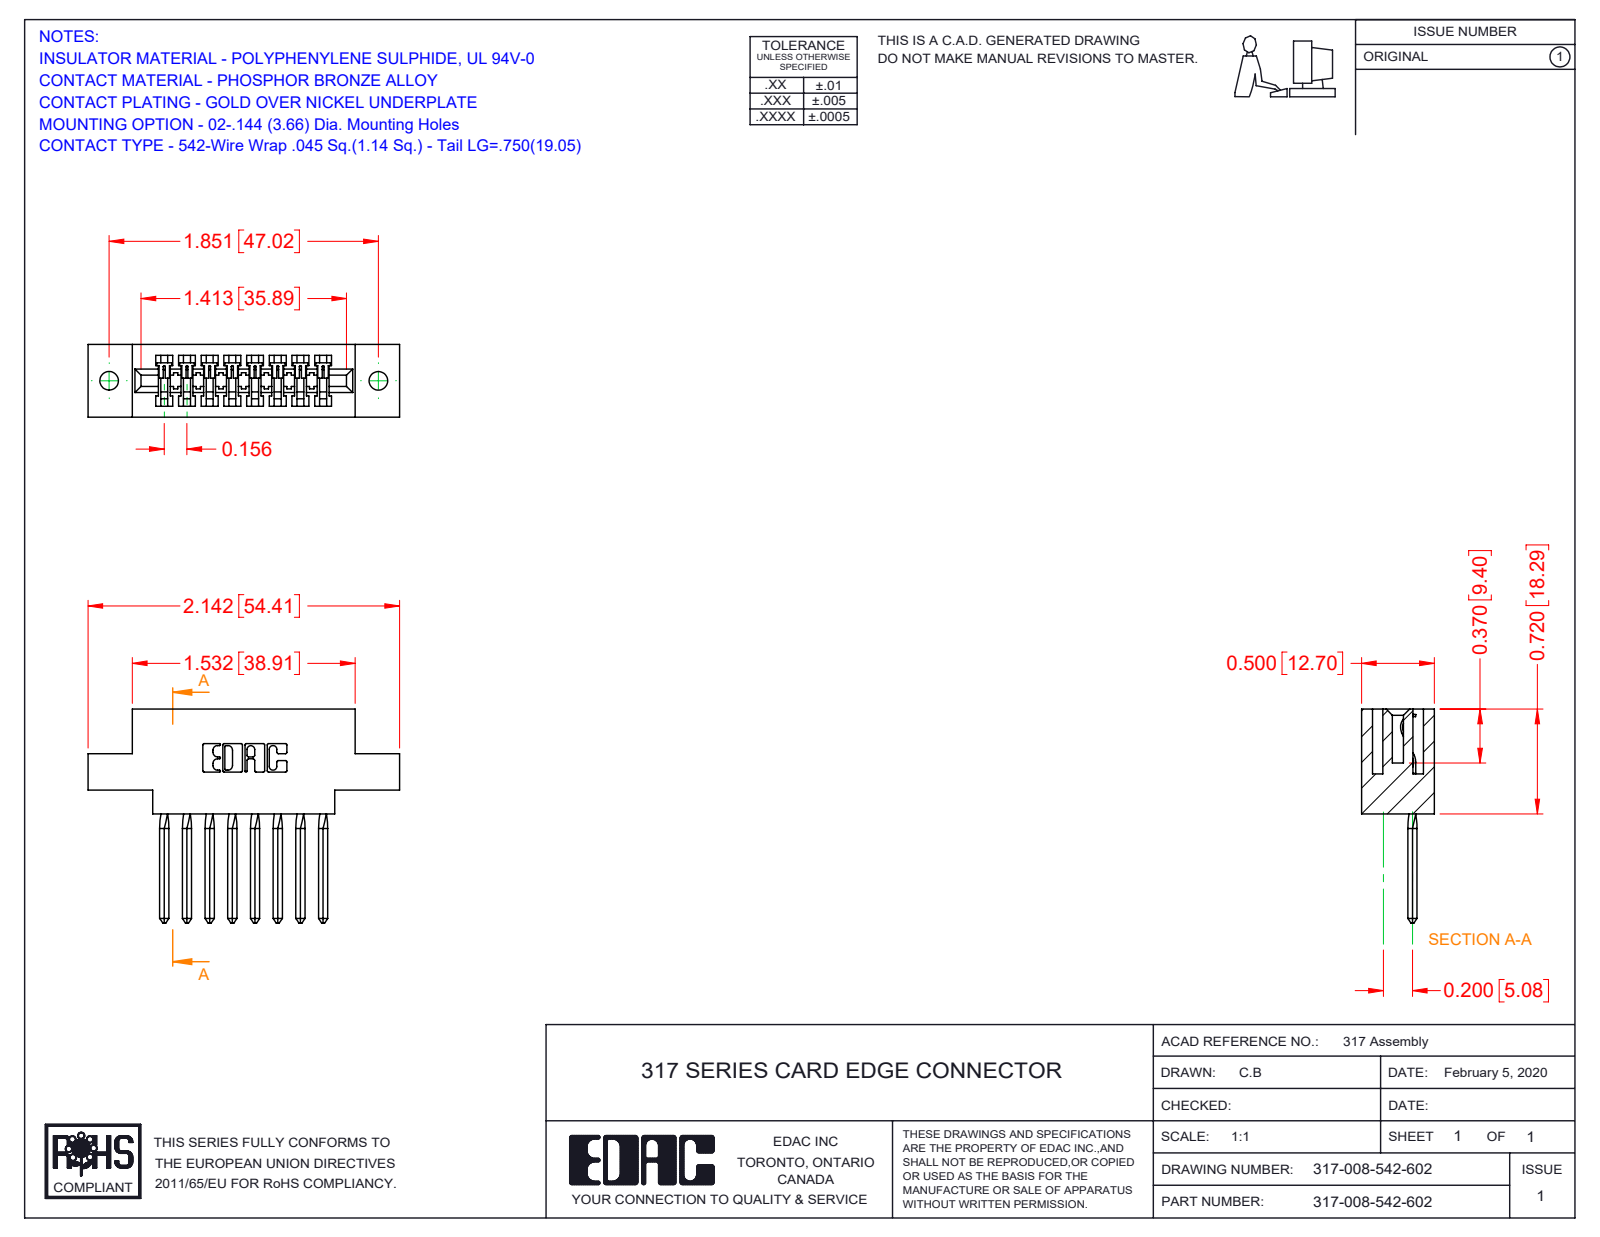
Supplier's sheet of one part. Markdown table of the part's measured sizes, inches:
| quantity | value |
| --- | --- |
| part name | 317-290-003_542; 317-008-542-602; 317 Part_.144 Dia |
| STEP written by | SolidWorks 2016 (CONFIG_CONTROL_DESIGN) |
| units | inches |
| bodies | 9 solids, 702 faces (570 planar, 100 cylindrical, 32 other) |
| overall size | 2.142 × 1.47 × 0.5 |
| volume | 0.455 in³ |
| surface area | 12.51 in² |
| round holes (diameter × count) | 0.128 × 2 |
| partial cylindrical surfaces (radius × count) | 0.01 × 22, 0.006 × 16, 0.007 × 6, 0.031 × 6, 0.026 × 3, 0.074 × 1, 0.089 × 1, 0.1 × 1 |
| main face-to-face distances | 0.5, 0.075, 0.425, 0.11, 0.065, 0.22, 0.156, 0.116, 0.35, 0.136 |
| hole center spacings | 1.851 |
